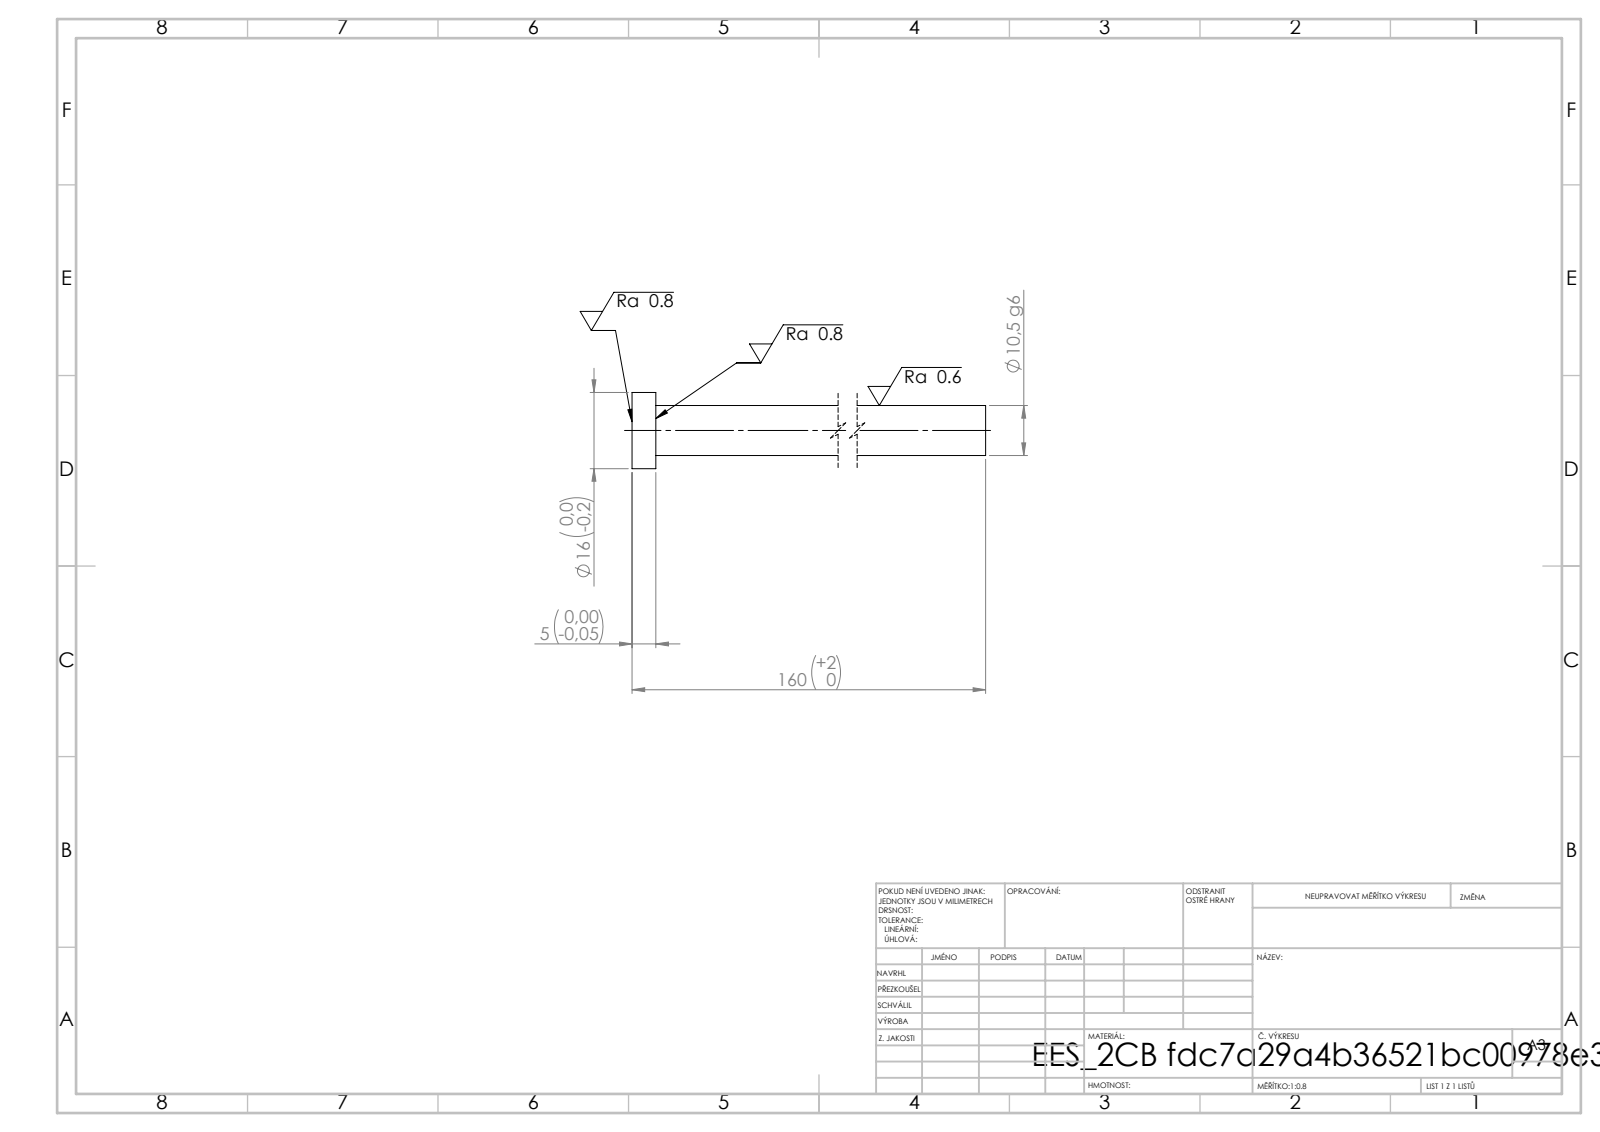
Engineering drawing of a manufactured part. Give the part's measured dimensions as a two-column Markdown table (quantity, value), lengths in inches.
| quantity | value |
| --- | --- |
| STEP written by | SolidWorks 2019 (CONFIG_CONTROL_DESIGN) |
| units | inches |
| bodies | 1 solid, 7 faces (3 planar, 4 cylindrical, 0 other) |
| overall size | 6.299 × 0.63 × 0.63 |
| volume | 0.88 in³ |
| surface area | 8.937 in² |
| round bosses / shafts (diameter × count) | 0.63 × 1, 0.413 × 1 |
| main face-to-face distances | 0.197, 6.299, 6.102 |
